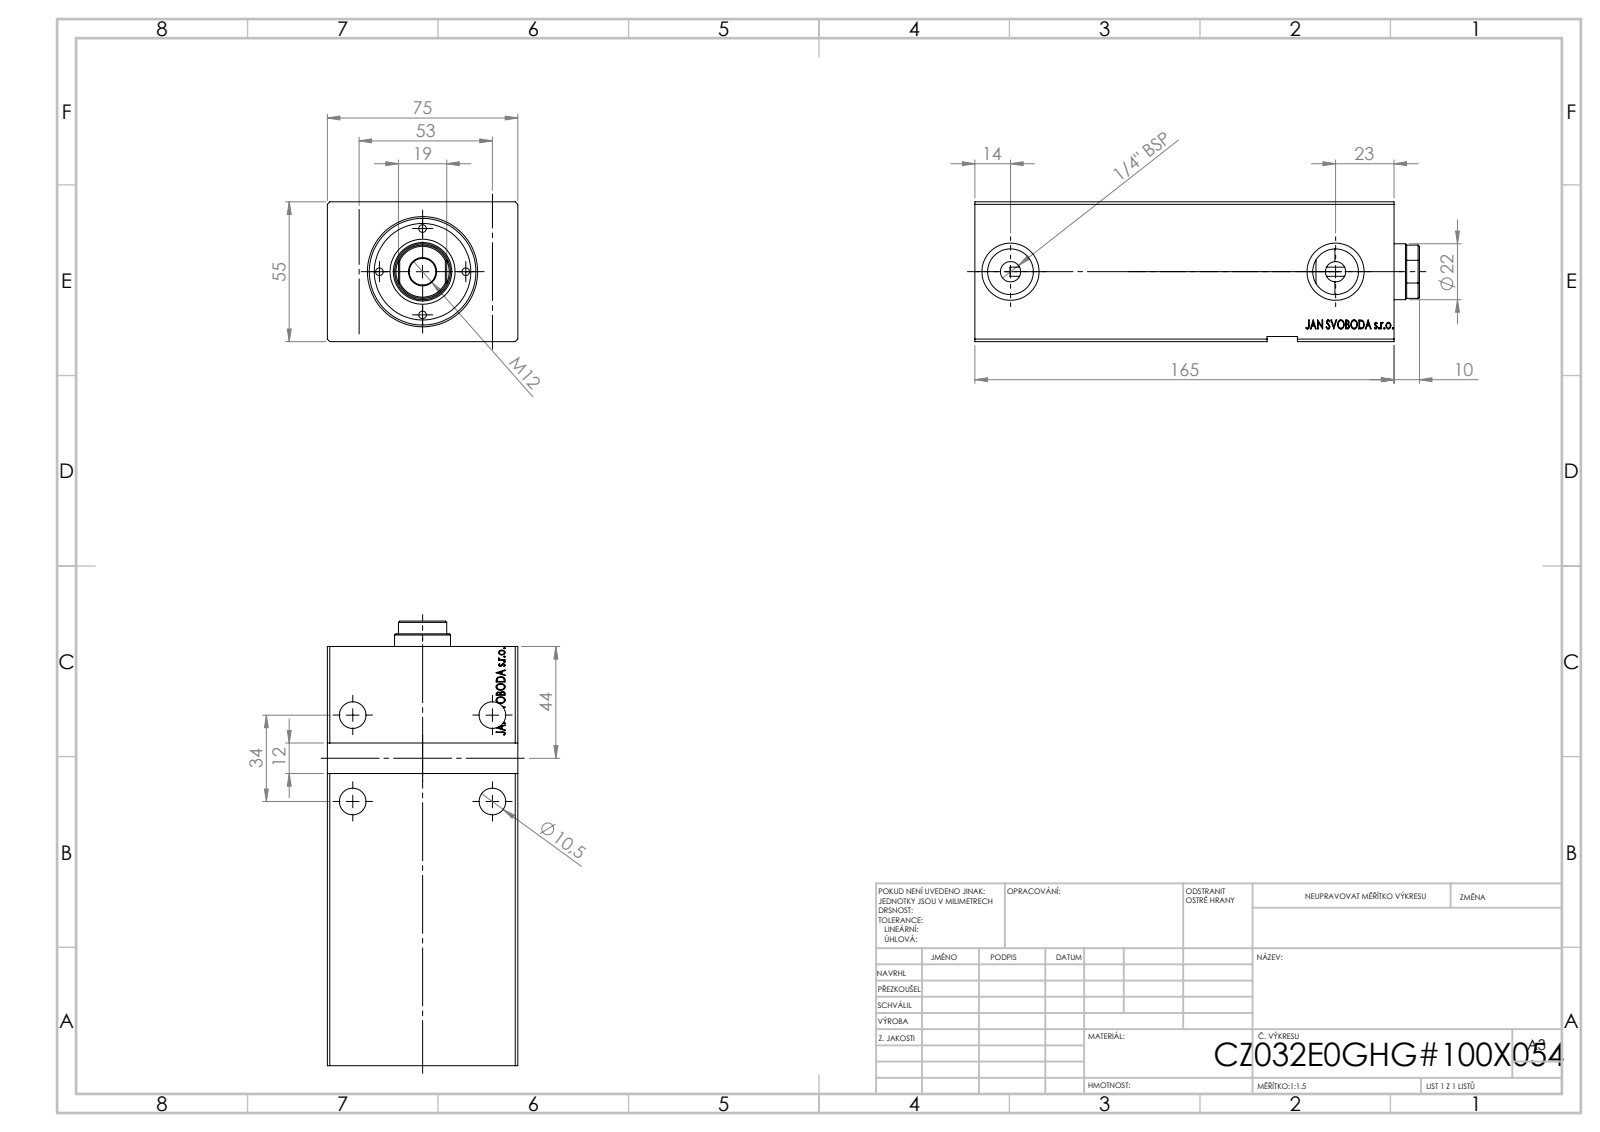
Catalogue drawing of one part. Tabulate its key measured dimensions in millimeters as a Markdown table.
| quantity | value |
| --- | --- |
| STEP written by | SolidWorks 2019 (CONFIG_CONTROL_DESIGN) |
| units | millimeters |
| bodies | 1 solid, 751 faces (367 planar, 32 cylindrical, 352 other) |
| overall size | 165 × 75 × 55 |
| volume | 525 155 mm³ |
| surface area | 74 429 mm² |
| round holes (diameter × count) | 8 × 4, 10.5 × 4, 18 × 2, 22.5 × 2, 32 × 1, 36 × 1, 42 × 1 |
| main face-to-face distances | 55, 75, 165, 13.6, 164.8, 2, 53, 151.2, 13.8, 10 |
| hole center spacings | 34, 55, 64.66, 18.5, 33.02, 37.98, 46.8, 81.89 |
